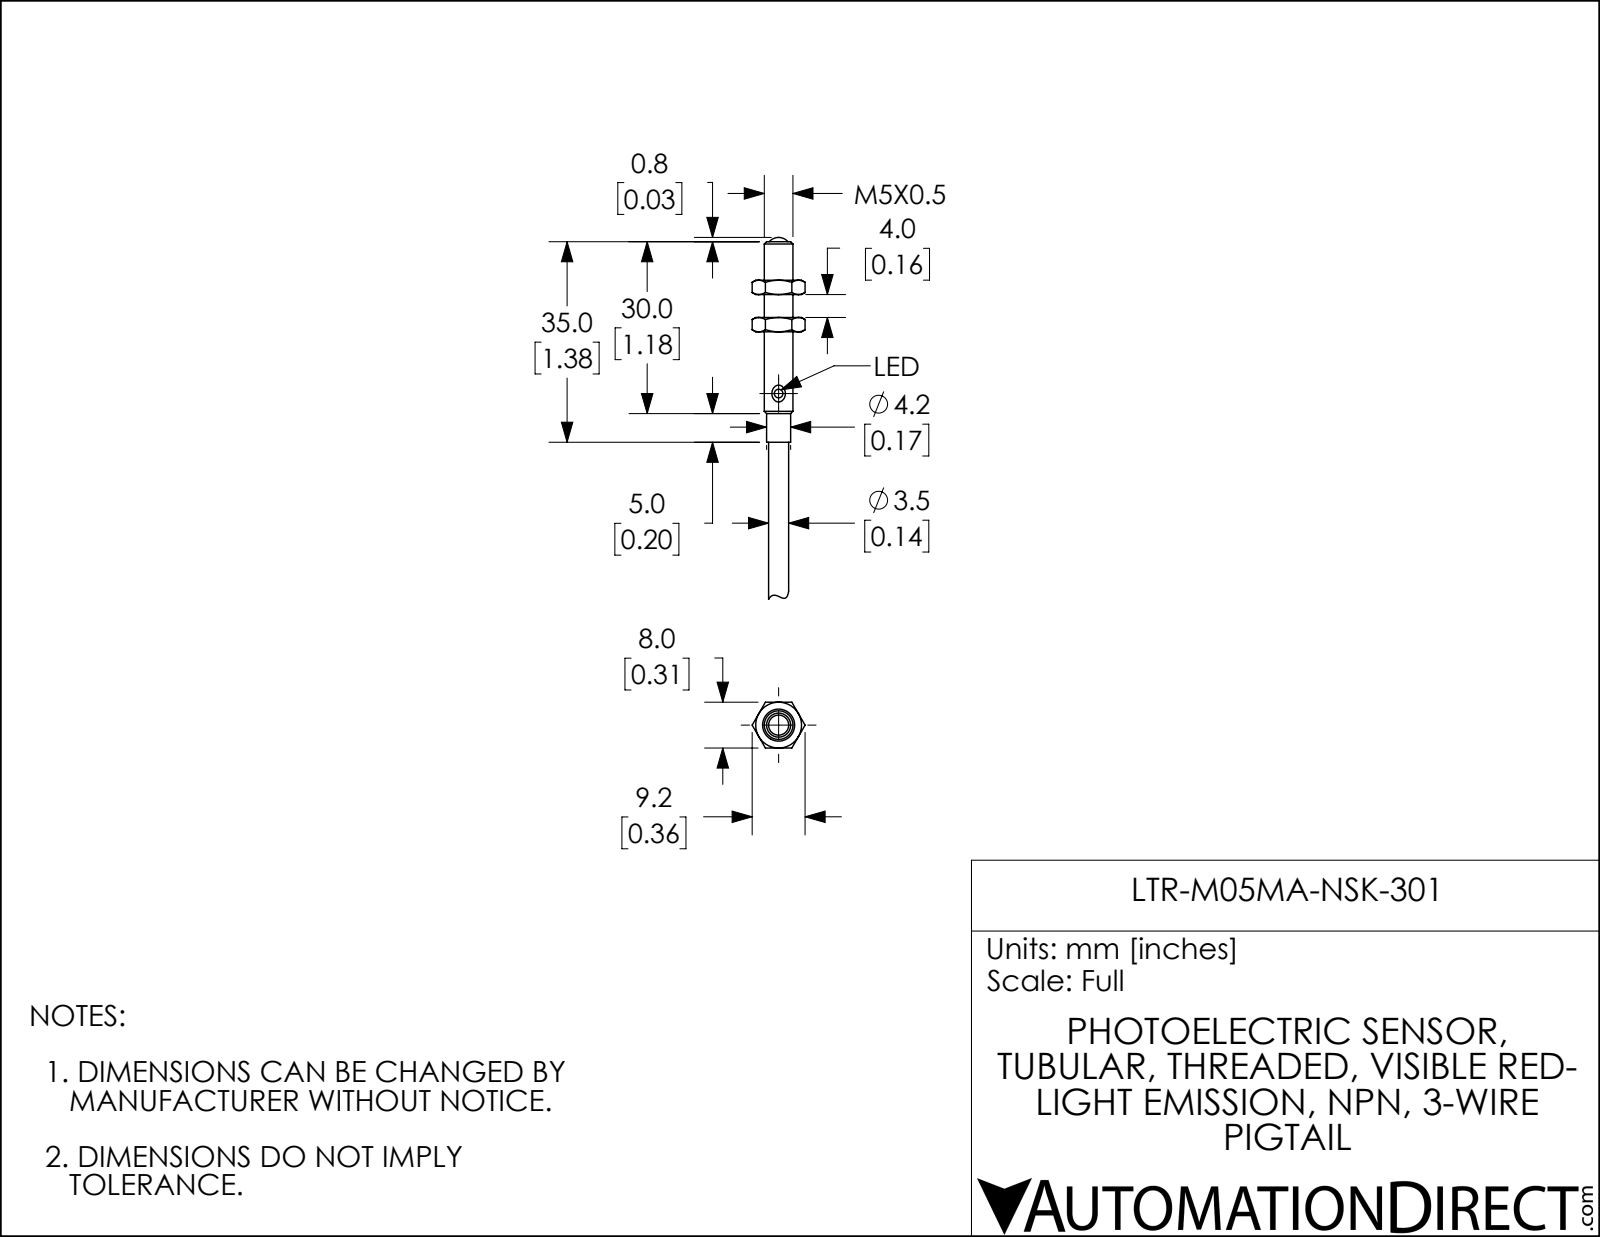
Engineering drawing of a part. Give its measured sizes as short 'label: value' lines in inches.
name: LxR-M05MA-Nxx
written by: SolidWorks 2018 (AUTOMOTIVE_DESIGN)
unit: in
bodies: 1 solid, 15 faces (3 planar, 7 cylindrical, 5 other)
size: 2.471 × 0.197 × 0.197
volume: 0.056 in³; area: 1.355 in²
holes: 1× ⌀0.059, 1× ⌀0.14
bosses: 1× ⌀0.197, 1× ⌀0.165, 1× ⌀0.138
face distances: 1.378, 1.362, 0.016
